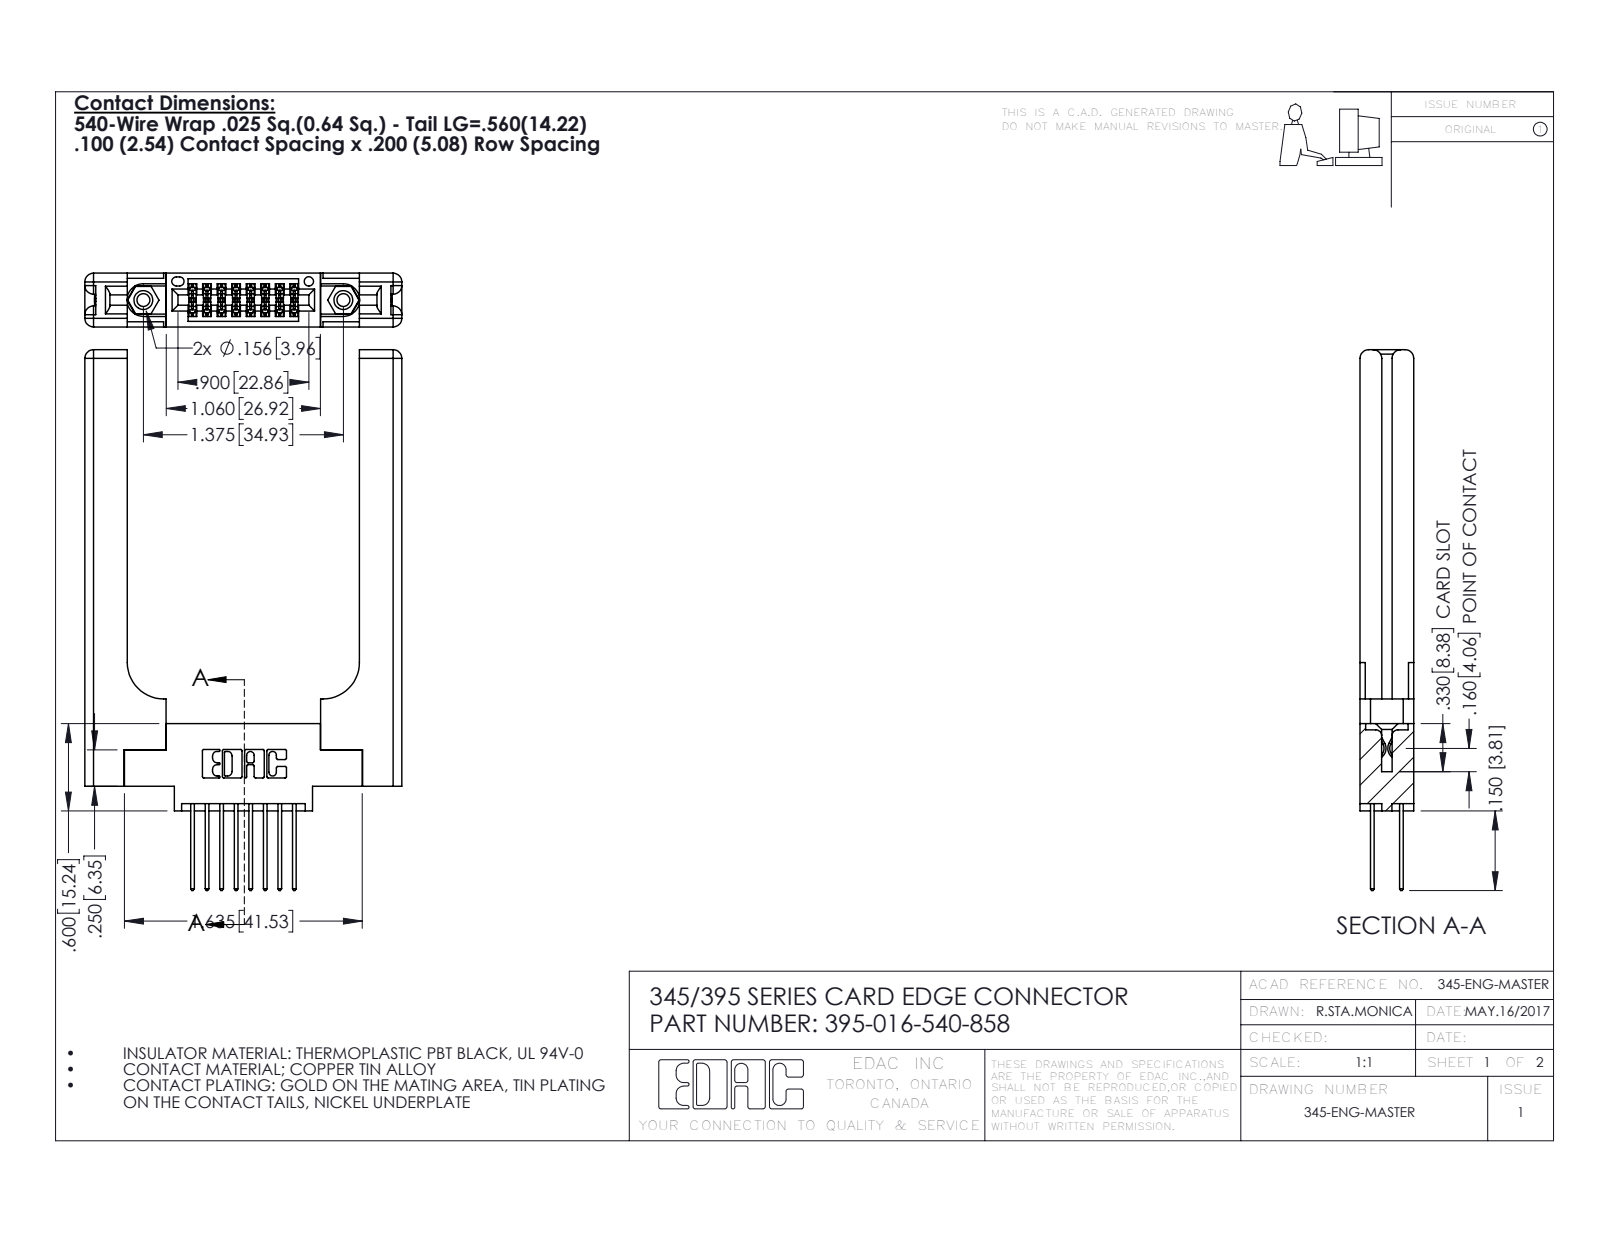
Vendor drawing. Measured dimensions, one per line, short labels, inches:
name: 395-016-540-858; 345-220-058_345-220-058; 345-292-001_345-293-140; 345 Part_0.170 Offset - 0.156 Dia-TH (+1 more)
written by: SolidWorks 2016 (CONFIG_CONTROL_DESIGN)
unit: in
bodies: 21 solids, 1186 faces (760 planar, 366 cylindrical, 60 other)
size: 3.717 × 2.179 × 0.37
volume: 0.823 in³; area: 18.95 in²
holes: 2× ⌀0.089, 2× ⌀0.125, 2× ⌀0.156, 1× ⌀0.064
bosses: 2× ⌀0.155
rounds: 24× R0.006, 22× R0.01, 16× R0.01, 16× R0.06, 6× R0.007, 6× R0.031, 3× R0.026, 2× R0.014
face distances: 0.37, 0.072, 0.15, 0.148, 0.077, 0.22, 0.298, 1.596, 0.225, 0.123
hole spacings: 0.27, 1.144, 1.375
